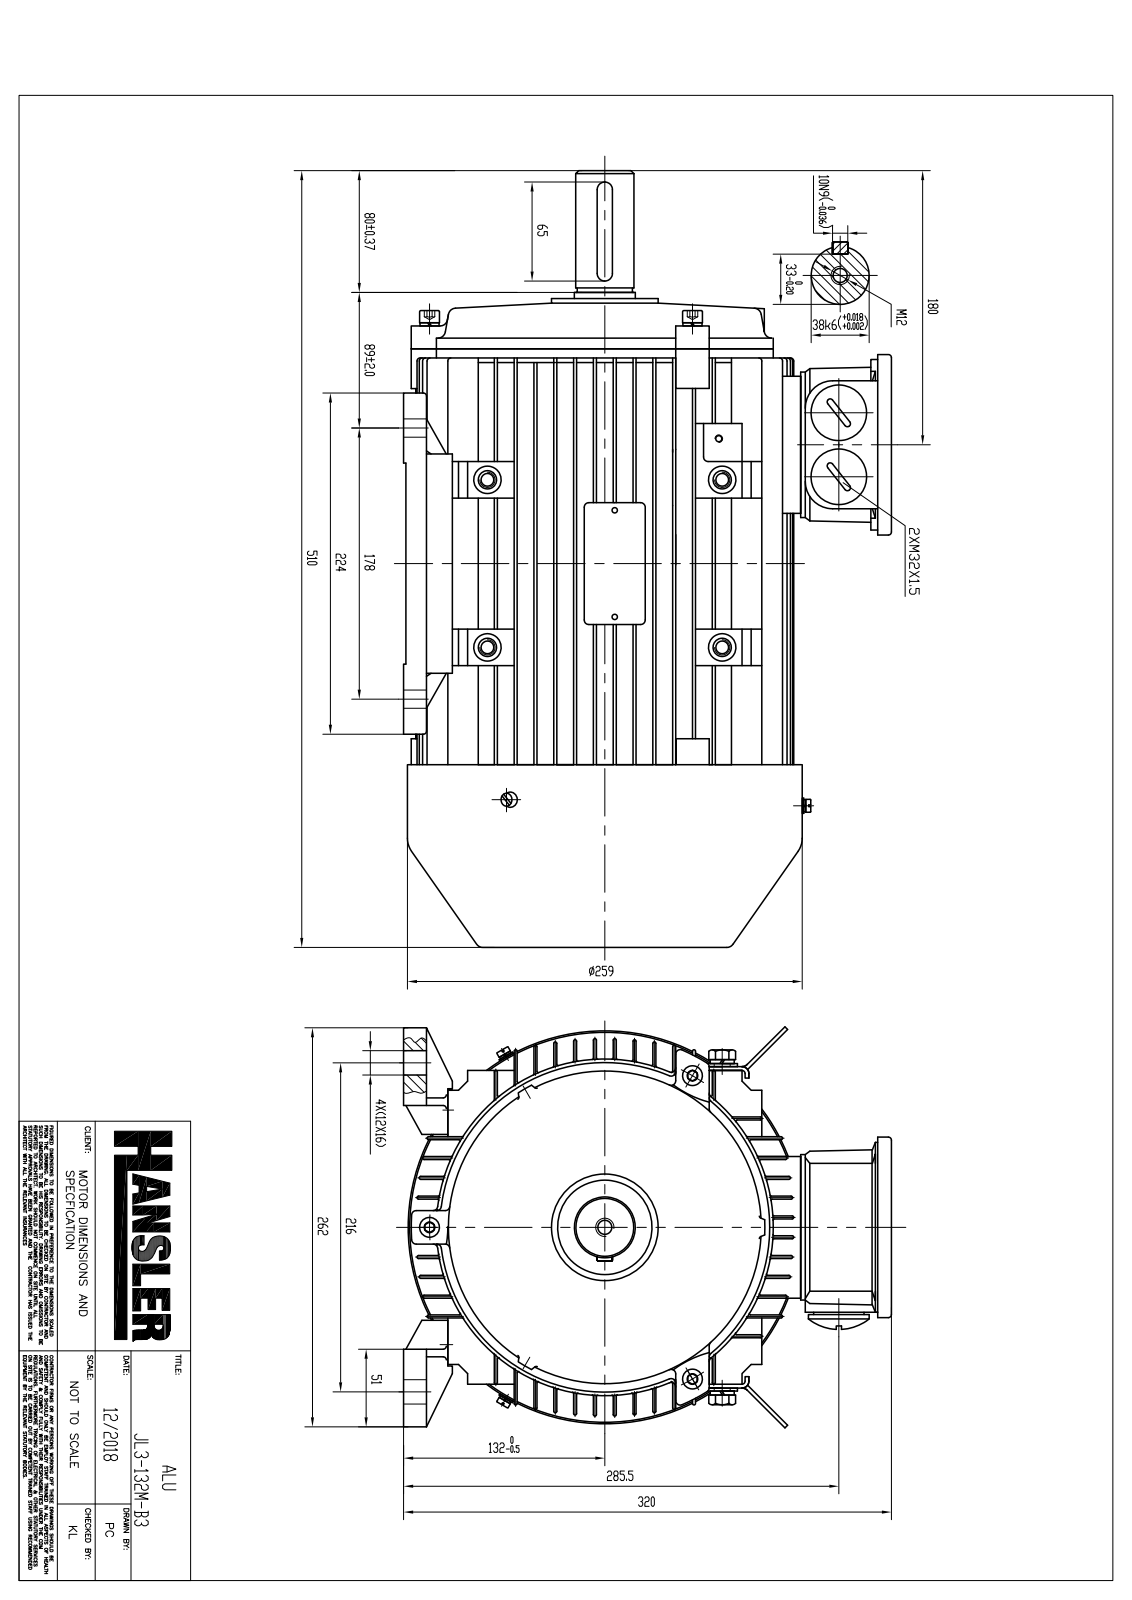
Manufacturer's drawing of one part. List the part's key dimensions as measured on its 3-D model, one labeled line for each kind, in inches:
Part name (STEP PRODUCT): JL3-132M-B3
STEP written by: SolidWorks 2018 (CONFIG_CONTROL_DESIGN)
Units: inches
Bodies: 63 solids, 5197 faces (2454 planar, 2177 cylindrical, 566 other)
Overall size (bounding box): 19.528 × 12.591 × 10.367
Volume: 212.3 in³ · Surface area: 2 753 in²
Round holes (diameter × count): ⌀0.197 ×24, ⌀0.394 ×14, ⌀0.115 ×12, ⌀0.709 ×8, ⌀0.228 ×6, ⌀0.433 ×6, ⌀0.207 ×5, ⌀0.209 ×5, ⌀0.117 ×4, ⌀0.217 ×4, ⌀0.315 ×4, ⌀0.335 ×4
Round bosses / shafts (diameter × count): ⌀0.15 ×16, ⌀0.394 ×9, ⌀0.63 ×8, ⌀0.472 ×8, ⌀0.217 ×6, ⌀0.309 ×5, ⌀0.176 ×5, ⌀0.669 ×4
Partial cylindrical surfaces — rounded edges, fillets, slot ends (radius × count): R0.02 ×816, R0.079 ×130, R0.118 ×46, R0.039 ×36, R0.157 ×26, R0.197 ×24, R0.098 ×18, R0.008 ×12
Main face-to-face distances: 0.512, 0.079, 1.024, 3.583, 4.094, 0.433, 0.591, 3.071, 1.535, 0.945
Hole centre spacings: 3.32, 0.409, 0.285, 0.499, 0.835, 2.677, 3.858, 4.621
